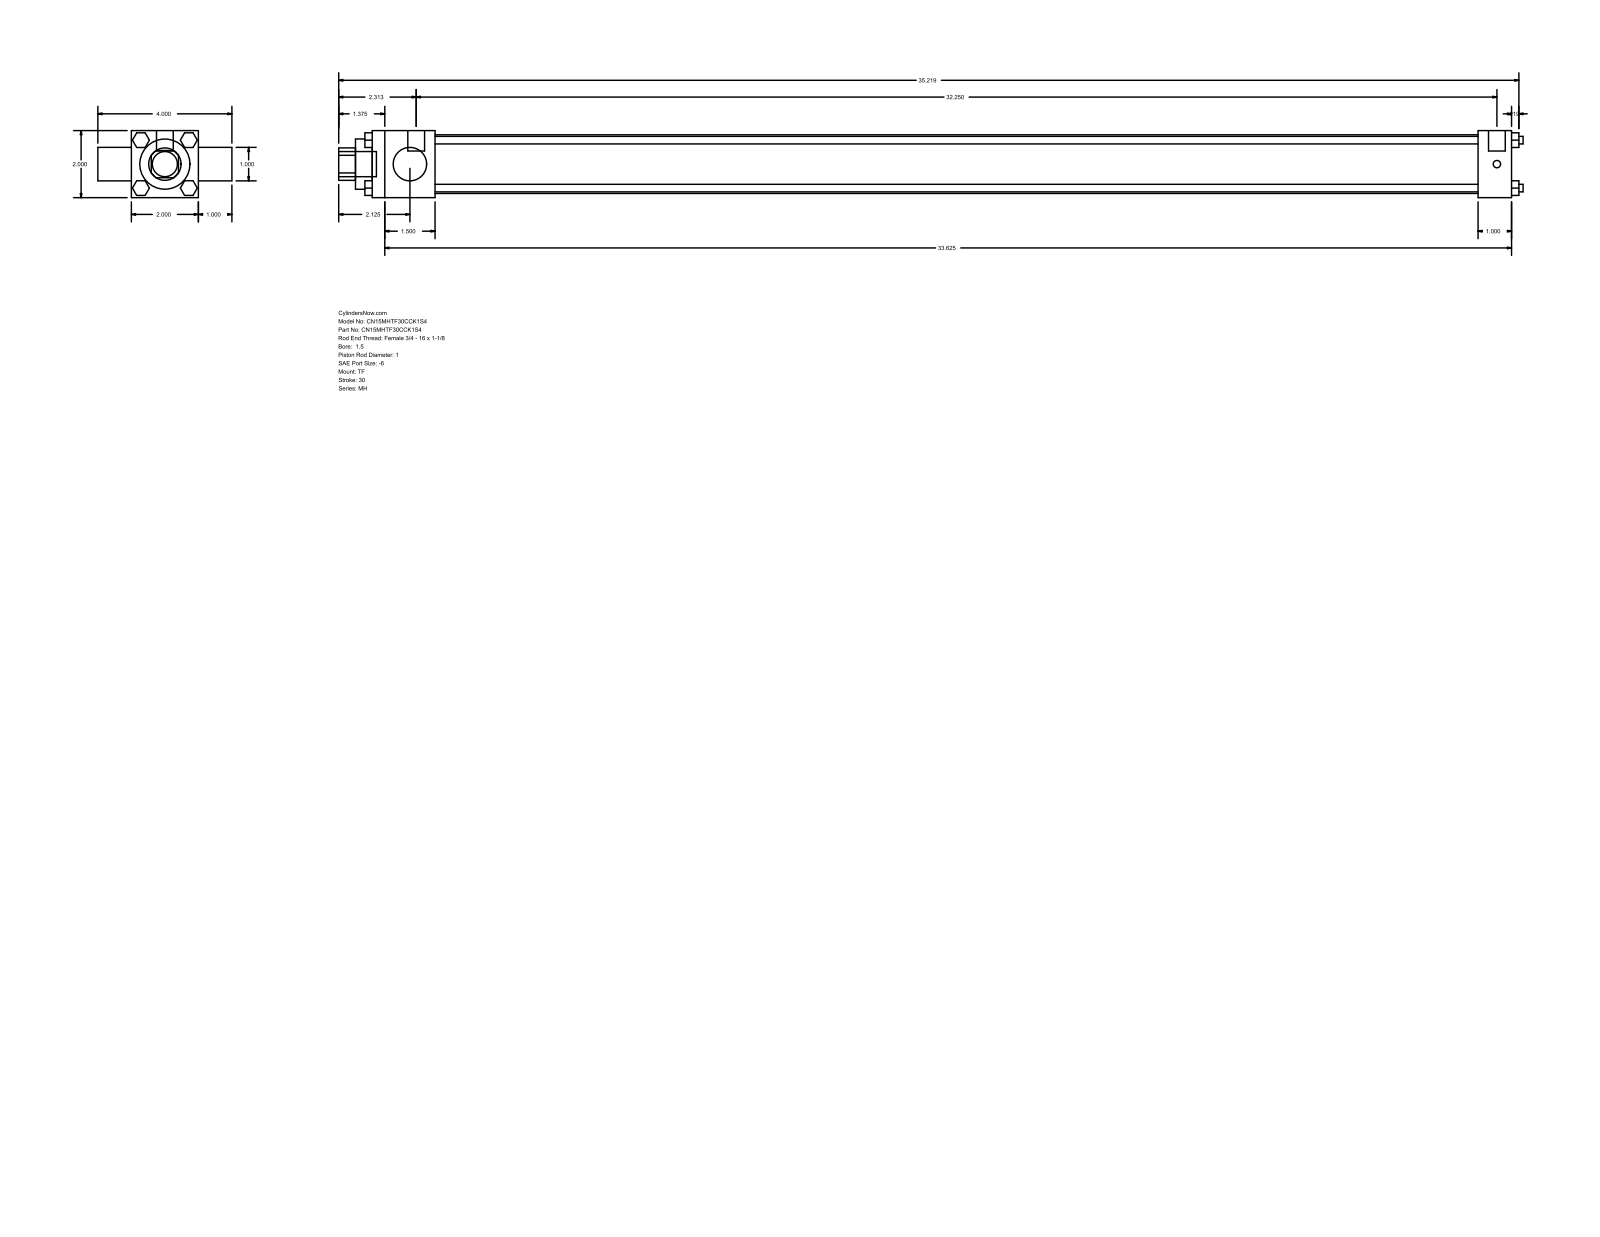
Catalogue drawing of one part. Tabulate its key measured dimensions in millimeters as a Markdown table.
| quantity | value |
| --- | --- |
| part name | MH_TF__0150_1 |
| STEP written by | GSSL Pune (CONFIG_CONTROL_DESIGN) |
| units | millimeters |
| bodies | 0 solids, 120 faces (92 planar, 28 cylindrical, 0 other) |
| overall size | 897.73 × 101.6 × 50.8 |
| round holes (diameter × count) | 25.4 × 2, 38.1 × 1, 44.45 × 1 |
| round bosses / shafts (diameter × count) | 5.71 × 4, 5.56 × 3, 12.7 × 2, 19.05 × 1 |
| partial cylindrical surfaces (radius × count) | 12.29 × 1 |
| main face-to-face distances | 50.8, 25.4, 863.6, 76.2, 47.63, 815.97, 838.2, 790.57, 869.16, 12.7 |
